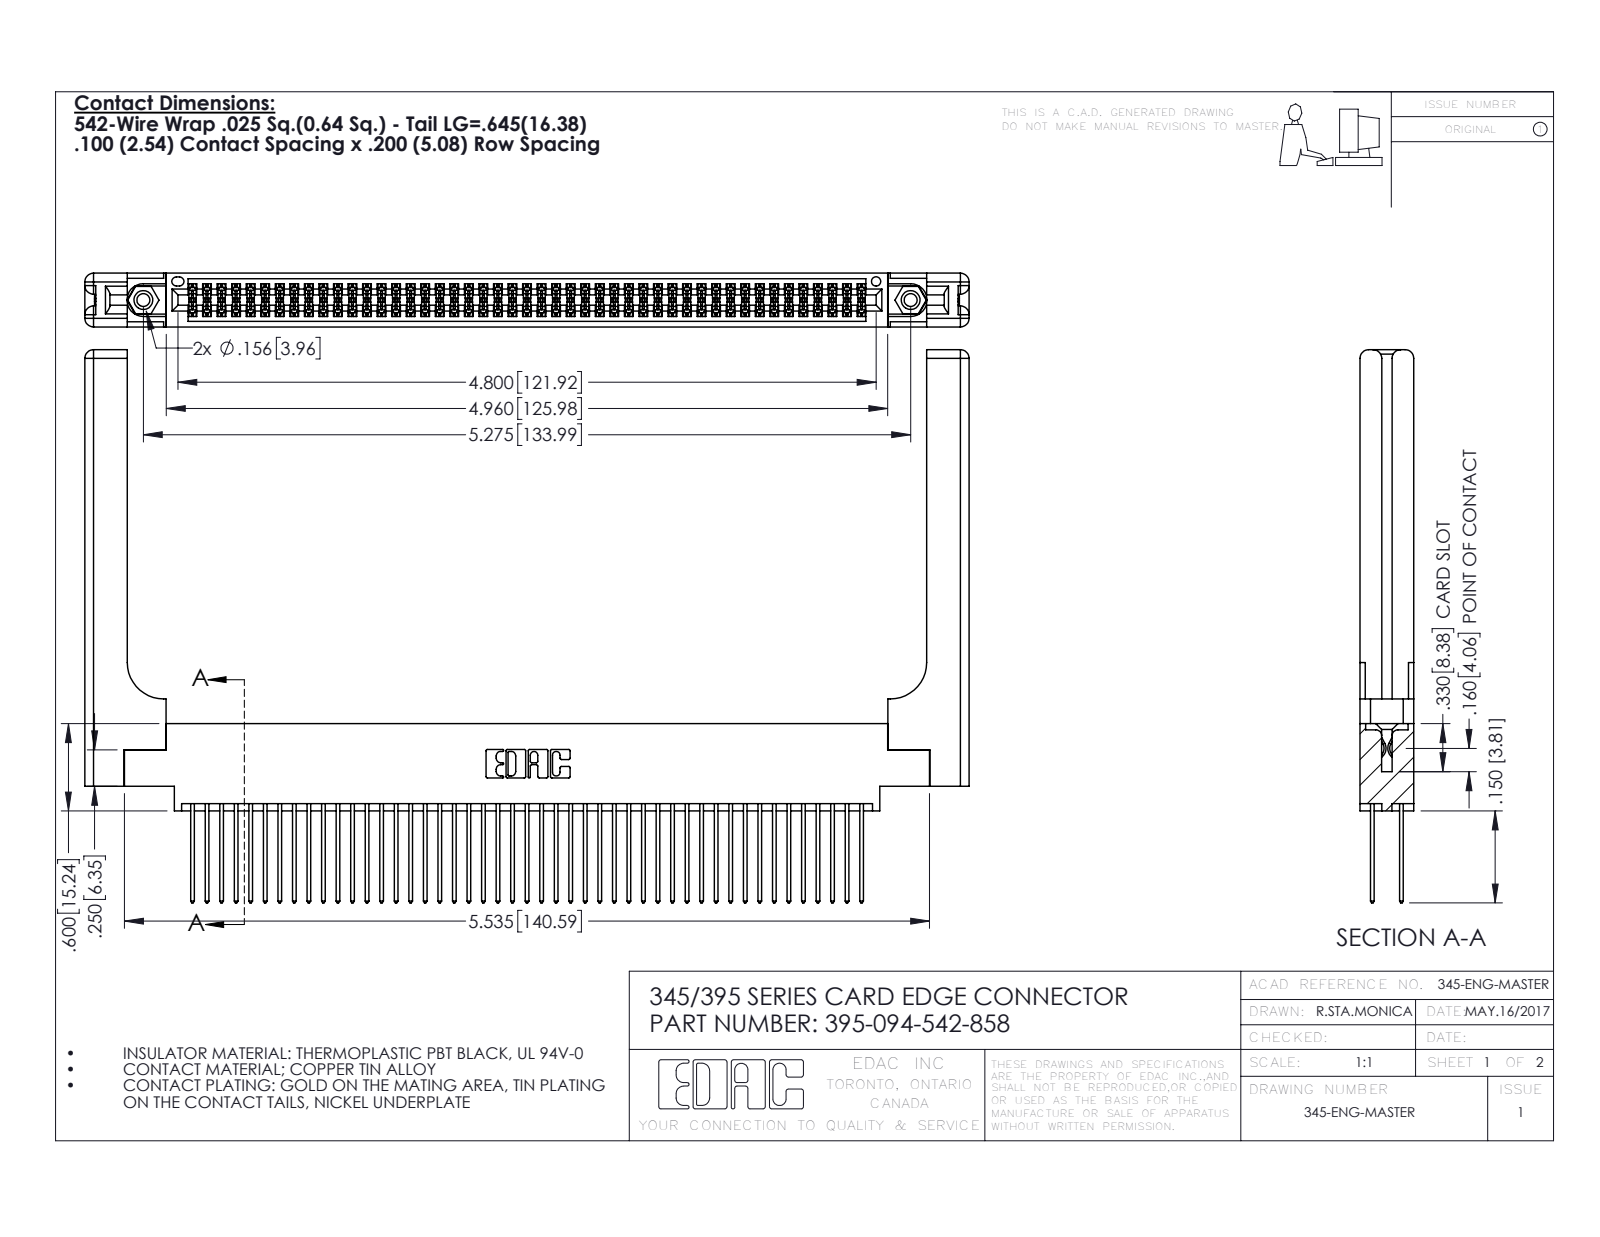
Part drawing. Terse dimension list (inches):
name: 345-220-058_345-220-058; 345-250-001_345-250-001-102; 395-094-542-858; 345-292-001_345-293-142 (+1 more)
written by: SolidWorks 2016 (CONFIG_CONTROL_DESIGN)
unit: in
bodies: 99 solids, 5086 faces (3334 planar, 1692 cylindrical, 60 other)
size: 6.079 × 3.802 × 0.37
volume: 1.455 in³; area: 46.6 in²
holes: 2× ⌀0.089, 2× ⌀0.125, 2× ⌀0.156, 1× ⌀0.064
bosses: 2× ⌀0.155
rounds: 141× R0.006, 94× R0.01, 22× R0.01, 16× R0.06, 6× R0.007, 6× R0.031, 3× R0.026, 2× R0.014
face distances: 0.072, 0.298, 0.37, 0.098, 0.272, 0.025, 0.2, 0.225, 0.175, 0.148
hole spacings: 0.27, 5.039, 5.275
